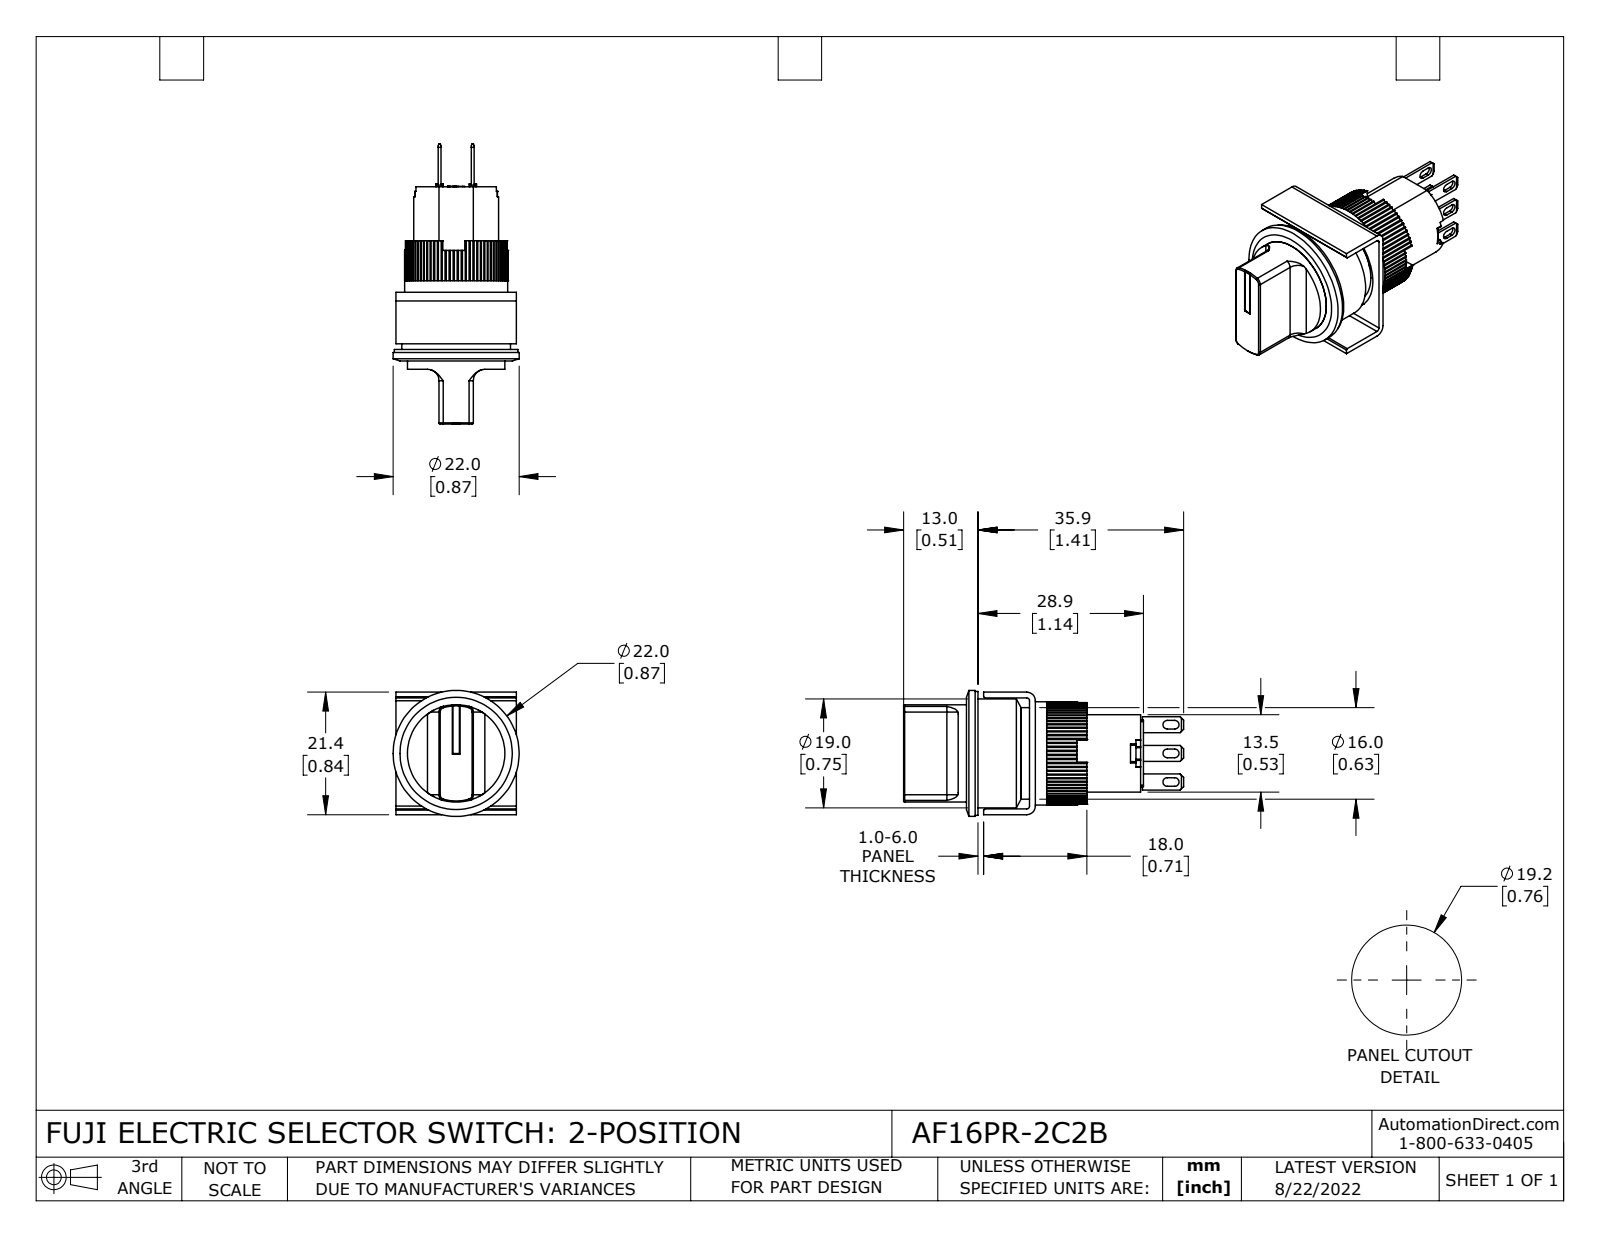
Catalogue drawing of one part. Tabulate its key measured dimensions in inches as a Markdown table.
| quantity | value |
| --- | --- |
| part name | AF16PR-2C2B |
| STEP written by | SolidWorks 2021 (CONFIG_CONTROL_DESIGN) |
| units | inches |
| bodies | 12 solids, 709 faces (505 planar, 189 cylindrical, 15 other) |
| overall size | 1.925 × 0.866 × 0.866 |
| volume | 0.493 in³ |
| surface area | 10.41 in² |
| round holes (diameter × count) | 0.039 × 1, 0.669 × 1, 0.709 × 1, 0.748 × 1 |
| round bosses / shafts (diameter × count) | 0.866 × 1, 0.85 × 1, 0.63 × 1, 0.583 × 1 |
| partial cylindrical surfaces (radius × count) | 0.01 × 80, 0.008 × 14, 0.03 × 6, 0.039 × 4, 0.02 × 2, 0.059 × 2, 0.079 × 2, 0.331 × 1 |
| main face-to-face distances | 0.374, 0.039, 0.059, 0.803, 0.764, 0.02, 0.433, 0.155, 0.648, 0.232 |
